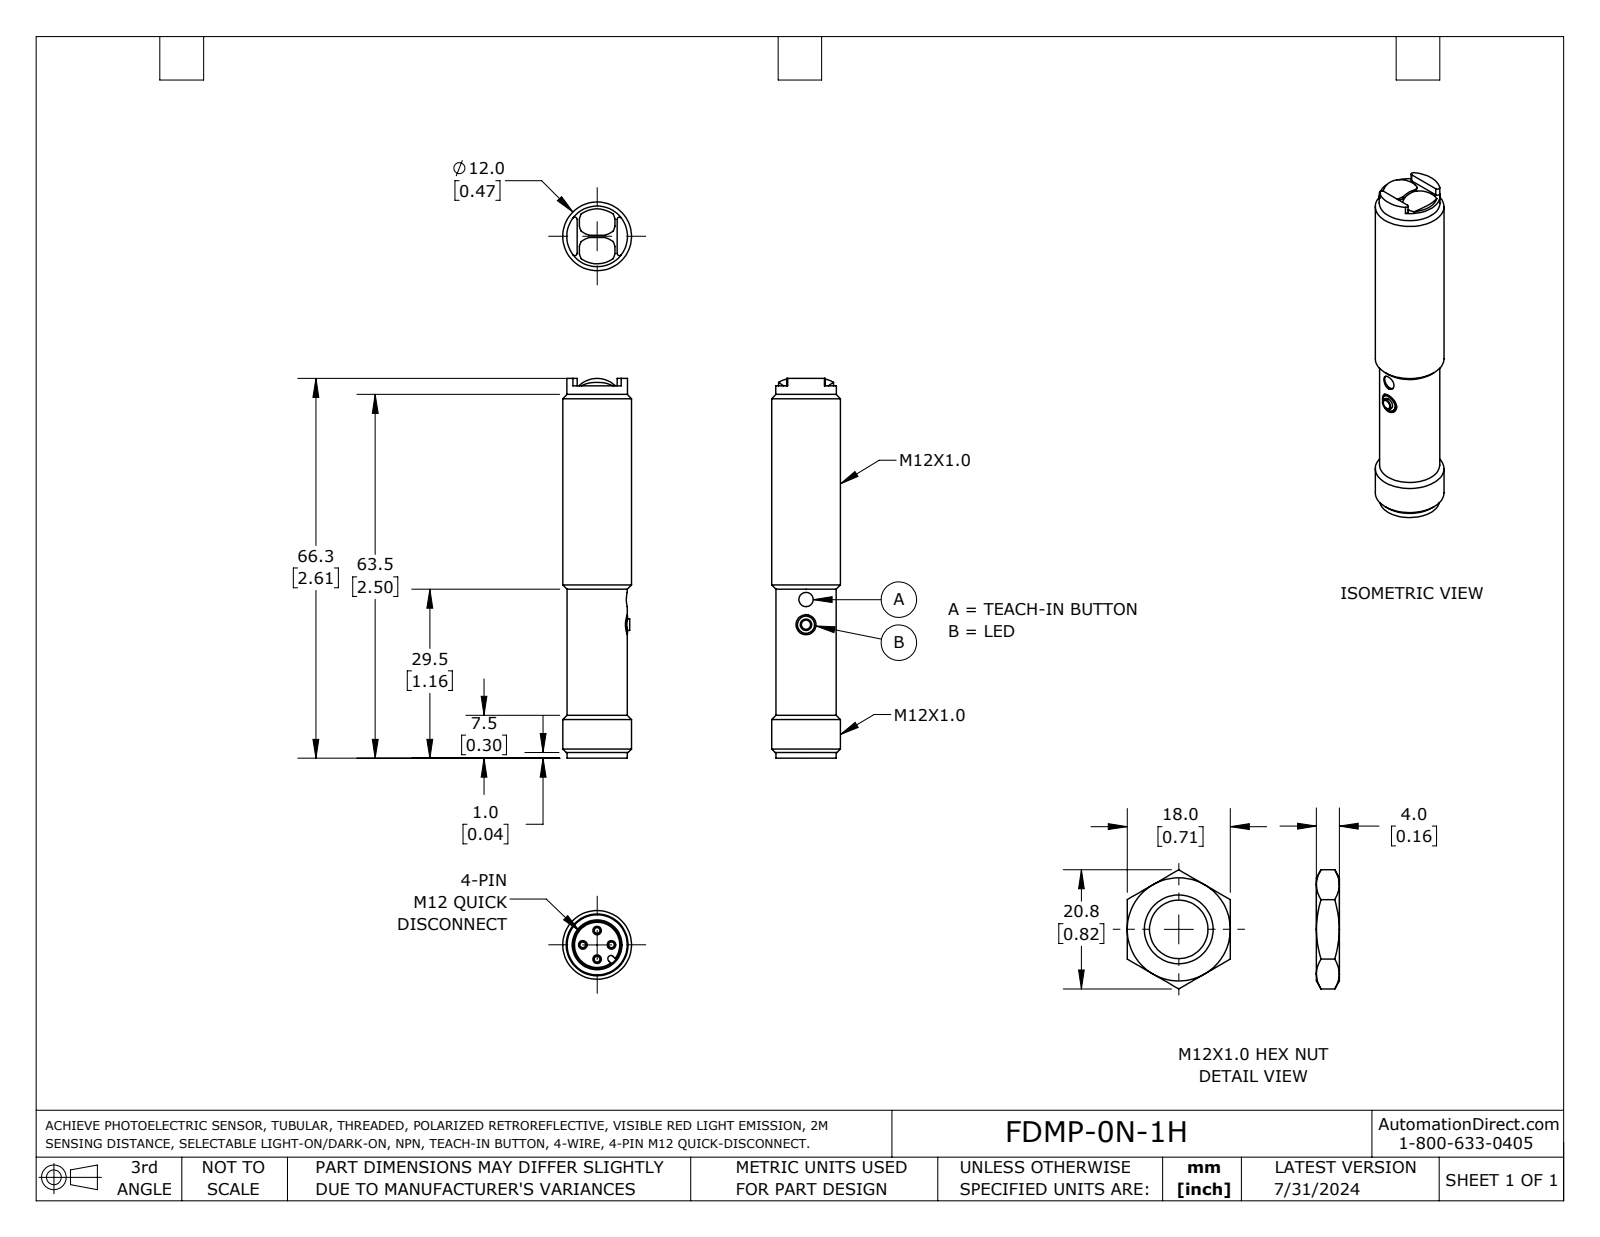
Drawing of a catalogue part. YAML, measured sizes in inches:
part_name: "DMP_1H_fig"
step_written_by: "SolidWorks 2023 (AUTOMOTIVE_DESIGN)"
units: inches
bodies: {solids: 1, faces: 64, planar: 20, cylindrical: 27, other: 17}
overall_size: [2.61, 0.472, 0.472]
volume: 0.386
surface_area: 4.575
round_holes:
  - {diameter: 0.098, count: 1}
  - {diameter: 0.138, count: 1}
  - {diameter: 0.327, count: 1}
round_bosses_or_shafts:
  - {diameter: 0.039, count: 4}
  - {diameter: 0.472, count: 1}
  - {diameter: 0.417, count: 1}
  - {diameter: 0.413, count: 1}
  - {diameter: 0.118, count: 1}
  - {diameter: 0.079, count: 1}
partial_cylinders:
  - {radius: 0.016, count: 4}
  - {radius: 0.189, count: 3}
  - {radius: 0.022, count: 1}
  - {radius: 0.193, count: 1}
face_to_face_distances: [0.35, 2.559, 2.209, 2.61, 2.26, 0.051, 0.276, 0.331, 0.043, 0.039]
hole_center_spacings: [0.173]
